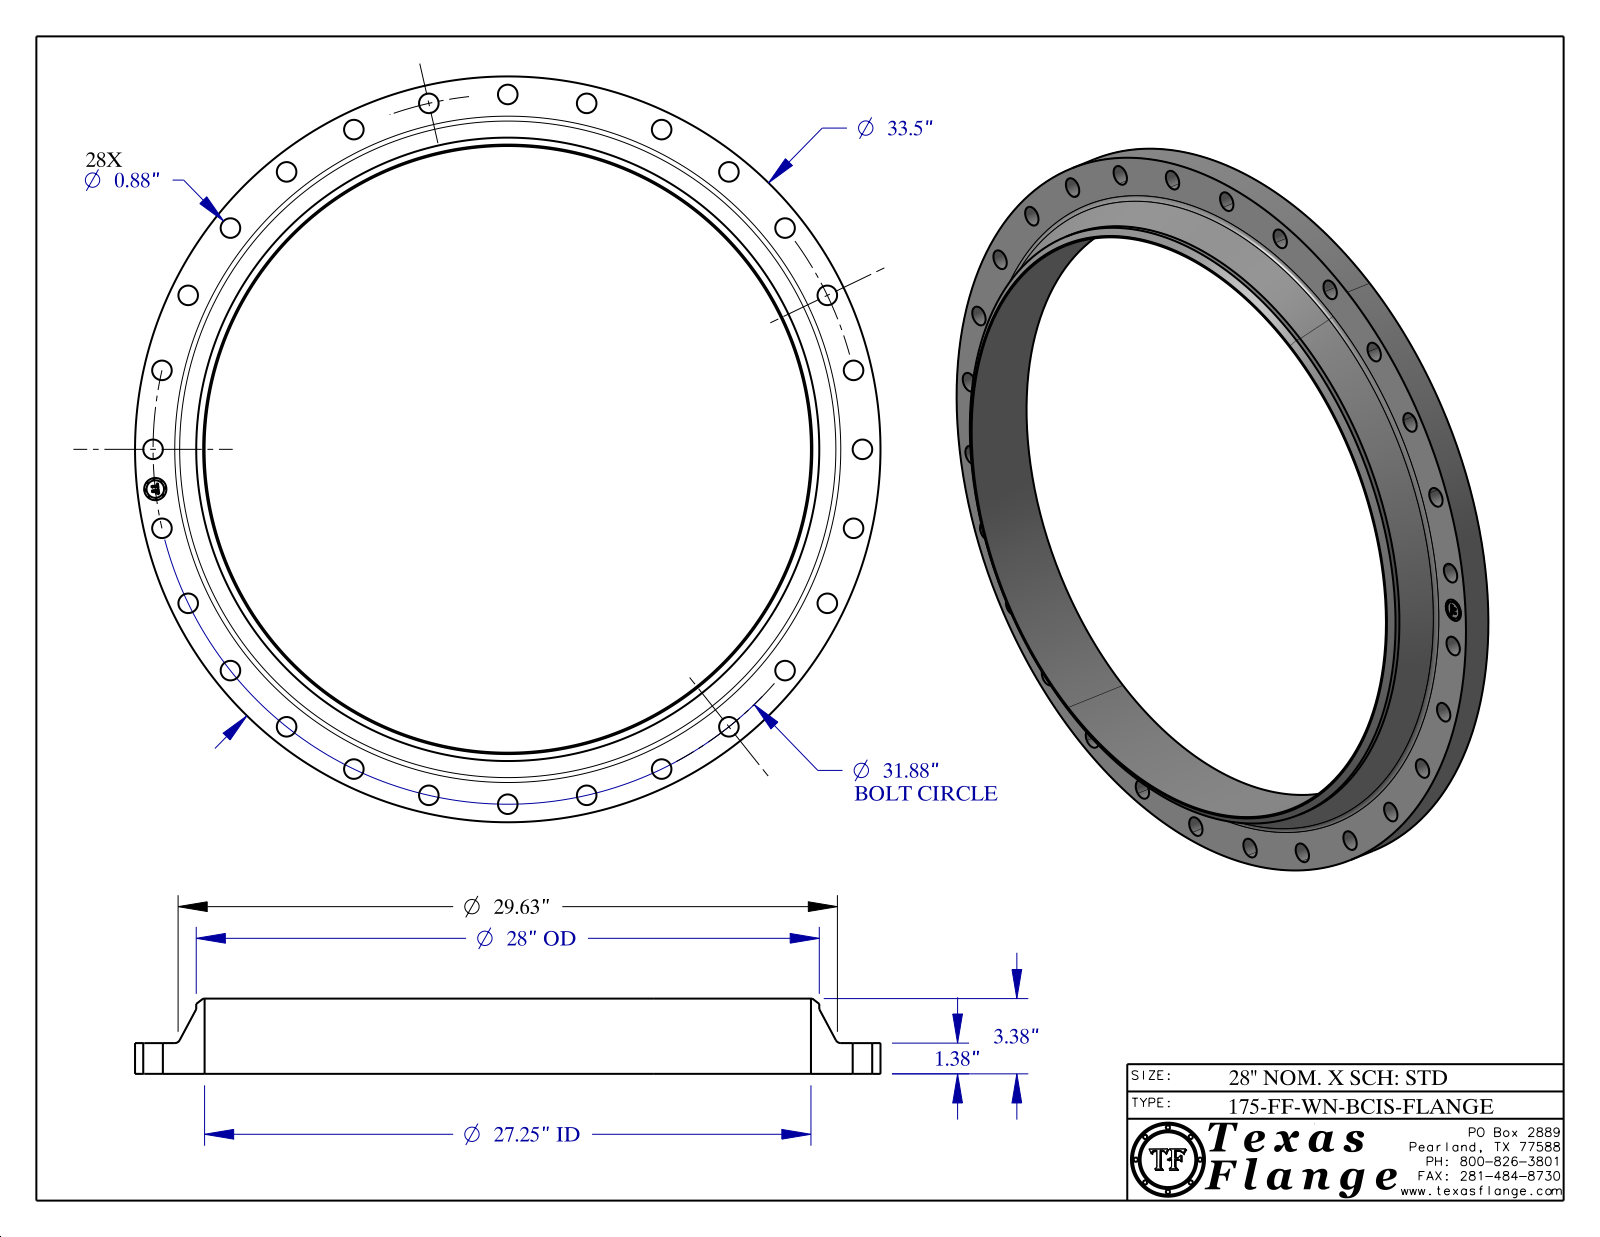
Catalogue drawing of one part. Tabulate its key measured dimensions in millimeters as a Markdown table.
| quantity | value |
| --- | --- |
| part name | 175-FF-WN, BCIS |
| STEP written by | CATIA V5 STEP AP214 (AUTOMOTIVE_DESIGN) |
| units | millimeters |
| bodies | 1 solid, 456 faces (368 planar, 82 cylindrical, 6 other) |
| overall size | 850.9 × 850.9 × 85.9 |
| volume | 8 290 000 mm³ |
| surface area | 781 900 mm² |
| round holes (diameter × count) | 22.4 × 28, 25.4 × 1, 692.2 × 1 |
| round bosses / shafts (diameter × count) | 1.5 × 8, 850.9 × 1, 711.2 × 1, 20 × 1 |
| main face-to-face distances | 35.1, 85.9, 50.8, 0.4, 34.7, 51.2, 7.6, 7.4, 1.4, 4.9 |
| hole center spacings | 764.3, 504.9, 633.1, 267.4, 351.3, 804.7, 90.7, 180.2 |
